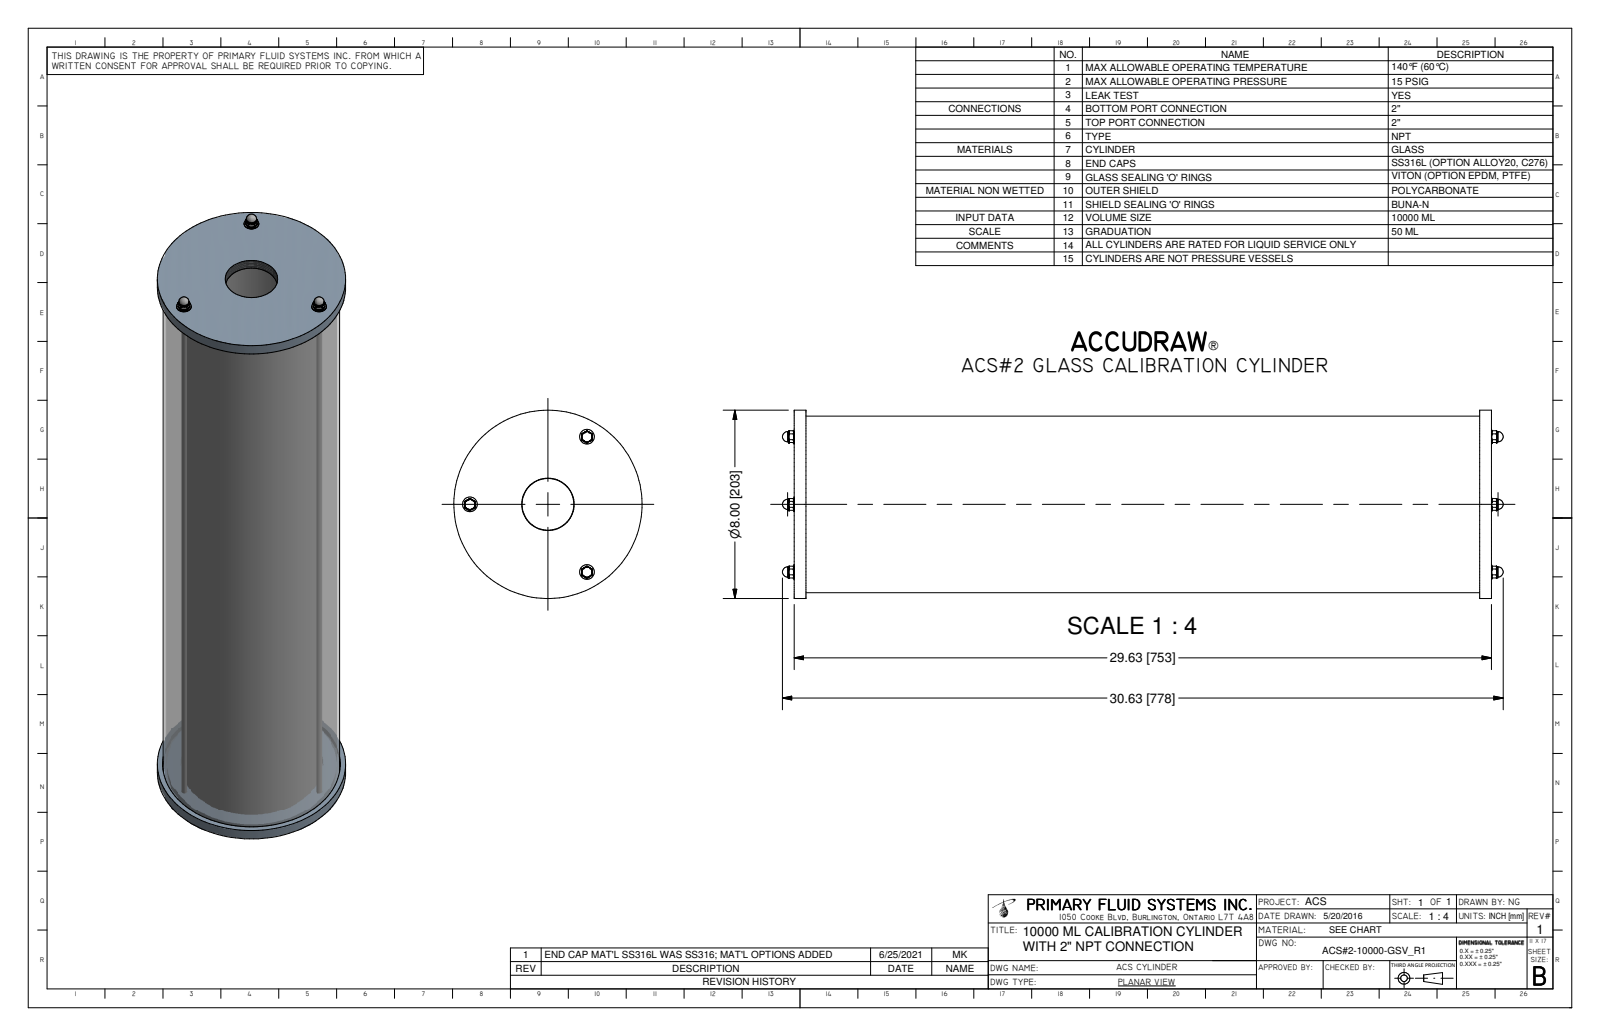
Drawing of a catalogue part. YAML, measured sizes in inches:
part_name: "ACS#2-10000-GSV_R0; ACS-3-10000-METAL_R3; ACS-2-10000_R6; ACS-1-10000-A_R0 (+3 more)"
step_written_by: "Autodesk Inventor 2009 (AUTOMOTIVE_DESIGN)"
units: inches
bodies: {solids: 19, faces: 425, planar: 38, cylindrical: 41, other: 346}
overall_size: [30.628, 8, 8]
volume: 230.2
surface_area: 2753
round_holes:
  - {diameter: 0.18, count: 3}
  - {diameter: 0.266, count: 3}
  - {diameter: 0.281, count: 3}
  - {diameter: 5.512, count: 1}
  - {diameter: 6.068, count: 1}
  - {diameter: 7.25, count: 1}
  - {diameter: 7.55, count: 1}
round_bosses_or_shafts:
  - {diameter: 0.625, count: 3}
  - {diameter: 0.25, count: 3}
  - {diameter: 8, count: 1}
  - {diameter: 7.5, count: 1}
  - {diameter: 7.2, count: 1}
  - {diameter: 5.906, count: 1}
  - {diameter: 5.427, count: 1}
face_to_face_distances: [29.628, 0.5, 29.128, 28.628, 0.125, 29.503, 0.375, 29.003, 0.225, 29.403]
hole_center_spacings: [3.317, 5.745, 5.745]
